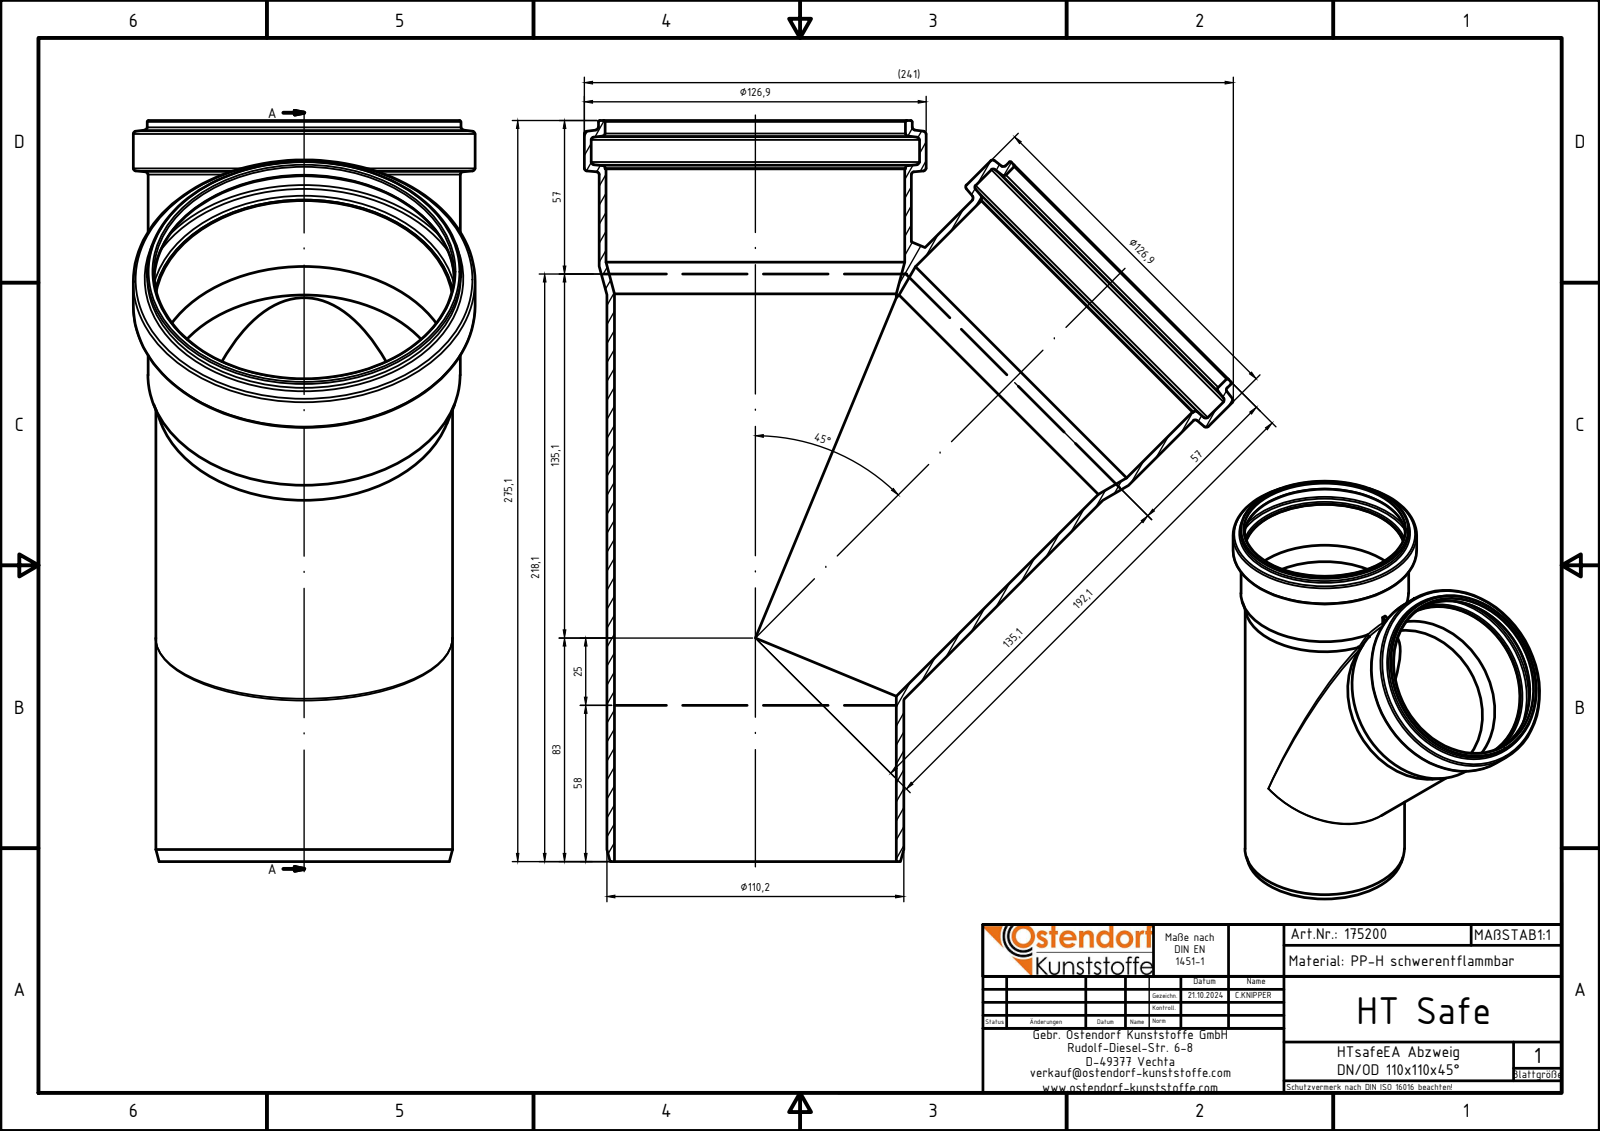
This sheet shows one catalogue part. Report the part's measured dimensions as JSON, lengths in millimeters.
{"part_name": "175200z", "step_written_by": "Autodesk Inventor 2024 (AUTOMOTIVE_DESIGN)", "units": "millimeters", "bodies": {"solids": 1, "faces": 68, "planar": 10, "cylindrical": 18, "other": 40}, "overall_size": [275.1, 240.92, 126.9], "volume_mm3": 364408, "surface_area_mm2": 270666, "round_holes": [[111.5, 3], [104.6, 2], [110.9, 2], [121.9, 2]], "round_bosses_or_shafts": [[126.9, 2], [116.5, 2], [115.9, 2], [110.2, 2]], "face_to_face_distances": [275.1, 17.99, 257.1, 18, 2.5, 5]}
